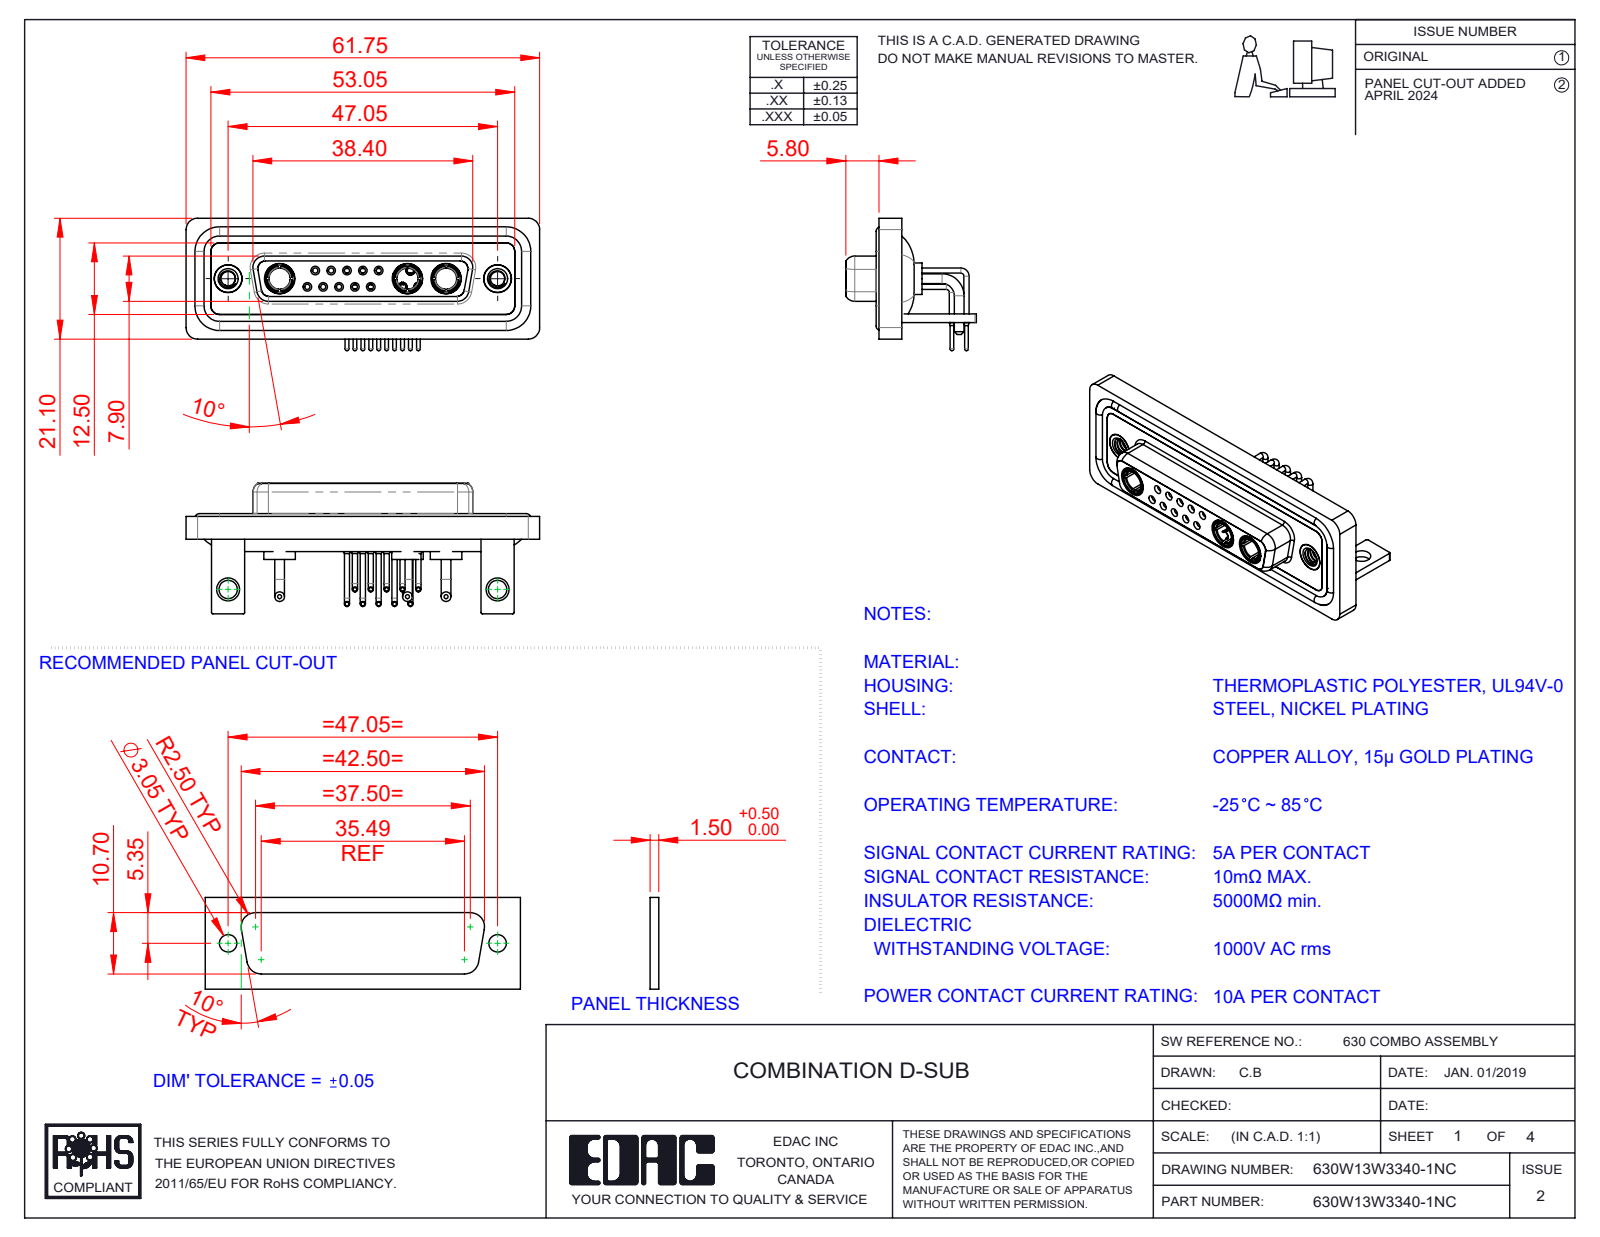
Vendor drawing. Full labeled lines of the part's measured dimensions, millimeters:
Part name (STEP PRODUCT): 630Combo Contact Row 2_50 Contacts; 630Combo Stabilizer Bracket_50 Contacts; 630Combo Housing_13W3; 630W13W3340-1NC (+6 more)
STEP written by: SolidWorks 2023 (CONFIG_CONTROL_DESIGN)
Units: millimetres
Bodies: 25 solids, 1192 faces (362 planar, 515 cylindrical, 315 other)
Overall size (bounding box): 61.75 × 23.12 × 22.8
Volume: 8 656 mm³ · Surface area: 14 883 mm²
Round holes (diameter × count): ⌀0.9 ×10, ⌀1.1 ×10, ⌀1.5 ×10, ⌀2 ×10, ⌀1.6 ×5, ⌀1.7 ×5, ⌀4.85 ×5, ⌀3.7 ×3, ⌀5.3 ×3, ⌀2.5 ×2, ⌀3.2 ×2, ⌀4 ×2
Round bosses / shafts (diameter × count): ⌀0.9 ×15, ⌀1.6 ×12, ⌀0.65 ×10, ⌀1.7 ×6, ⌀2 ×5, ⌀1.5 ×5, ⌀5.5 ×3, ⌀5.2 ×3
Partial cylindrical surfaces — rounded edges, fillets, slot ends (radius × count): R2 ×19, R1.5 ×18, R0.25 ×16, R1.35 ×8, R1.6 ×8, R0.5 ×5, R0.6 ×4, R0.65 ×4
Main face-to-face distances: 0.4, 1.8, 2.9, 1.5, 3.7, 4.1, 1.1, 1.4, 1.6, 3.1
Hole centre spacings: 3.16, 2.77, 5.54, 5.04, 8.31, 5.03, 7.49, 11.08
